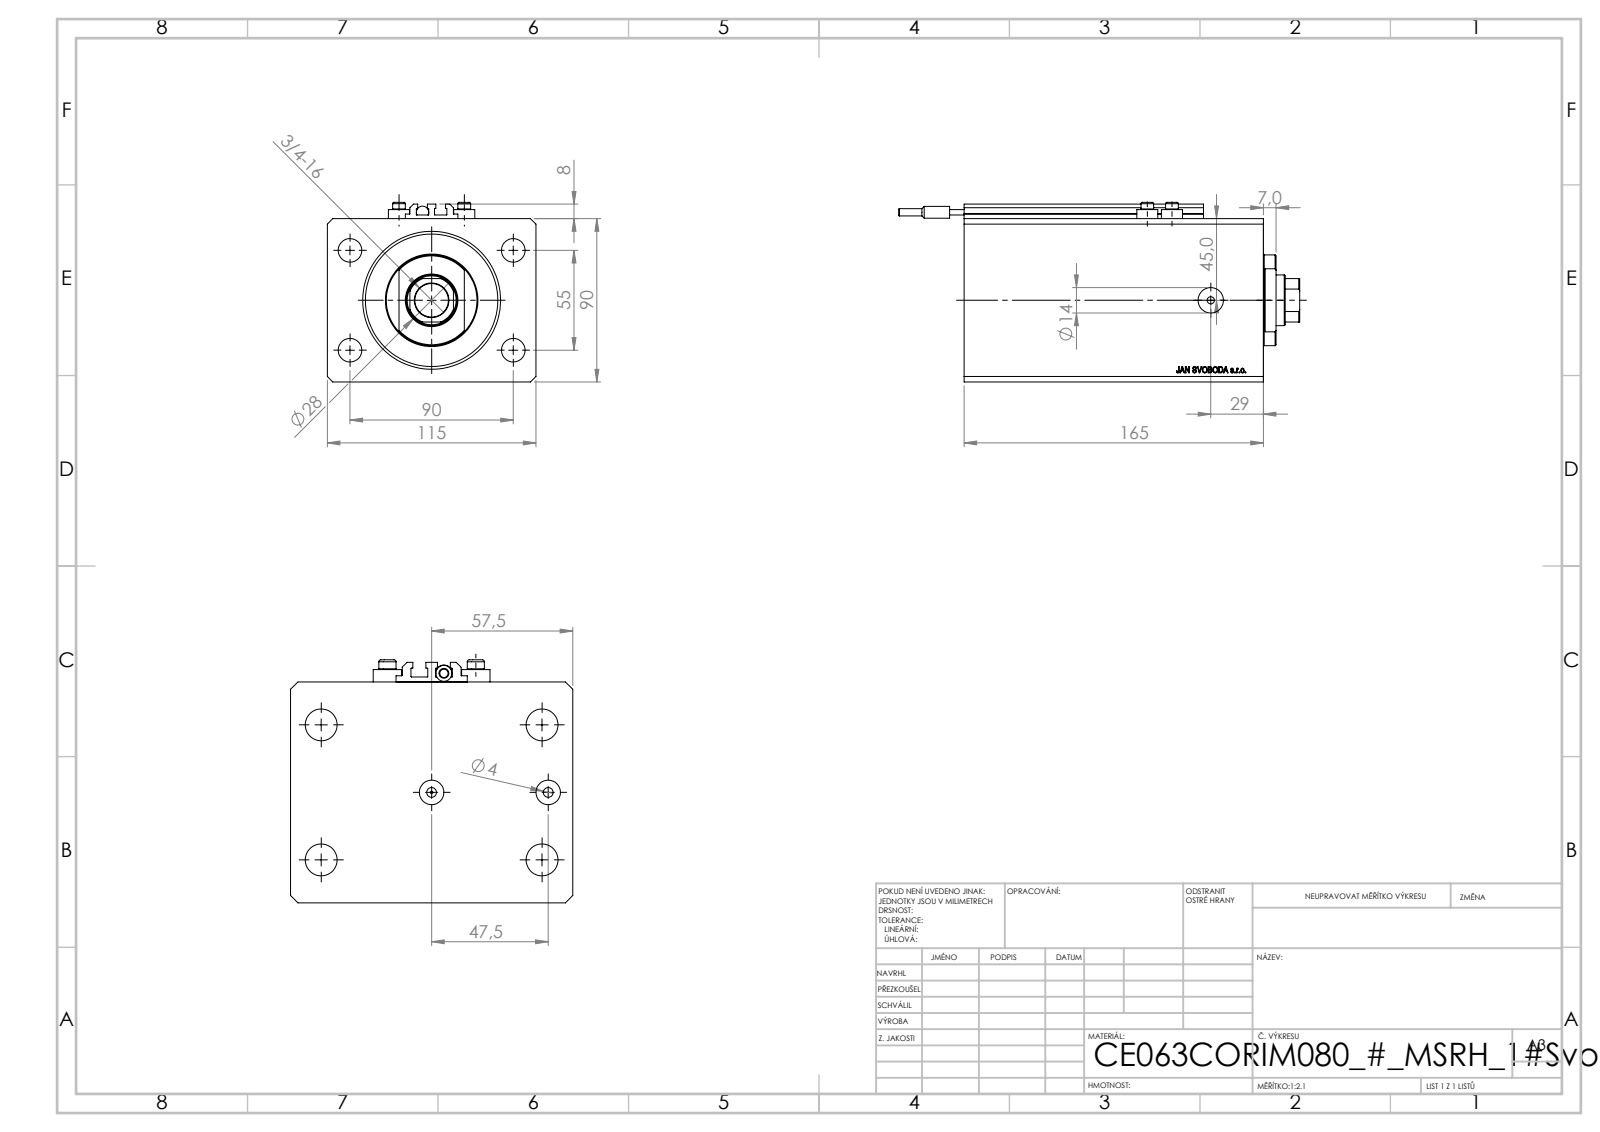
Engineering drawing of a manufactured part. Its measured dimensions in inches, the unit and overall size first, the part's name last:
Units: inches
Overall size (bounding box): 8.701 × 4.528 × 3.898
Round holes (diameter × count): ⌀0.157 ×8, ⌀0.512 ×4, ⌀0.394 ×2, ⌀0.551 ×2, ⌀0.049 ×1, ⌀0.728 ×1, ⌀1.102 ×1, ⌀2.48 ×1, ⌀2.992 ×1
Round bosses / shafts (diameter × count): ⌀0.457 ×4, ⌀0.276 ×4, ⌀1.969 ×1, ⌀0.268 ×1, ⌀0.256 ×1, ⌀0.157 ×1
Partial cylindrical surfaces — rounded edges, fillets, slot ends (radius × count): R0.008 ×10, R0.531 ×1
Main face-to-face distances: 3.543, 4.528, 6.496, 0.705, 5.791, 0.787, 5.709, 5.004, 2.559, 3.937
Hole centre spacings: 2.076, 0.535, 1.087, 1.417, 1.515, 2.165, 3.543, 3.799
Volume: 88.12 in³ · Surface area: 320.4 in²
Bodies: 9 solids, 1064 faces (520 planar, 94 cylindrical, 450 other)
Part name (STEP PRODUCT): V250CE_VC_C; ALLEN BOLT V250CE; V250CE_C_Body; SWITCH_V250CE (+1 more)
STEP written by: SolidWorks 2019 (CONFIG_CONTROL_DESIGN)
